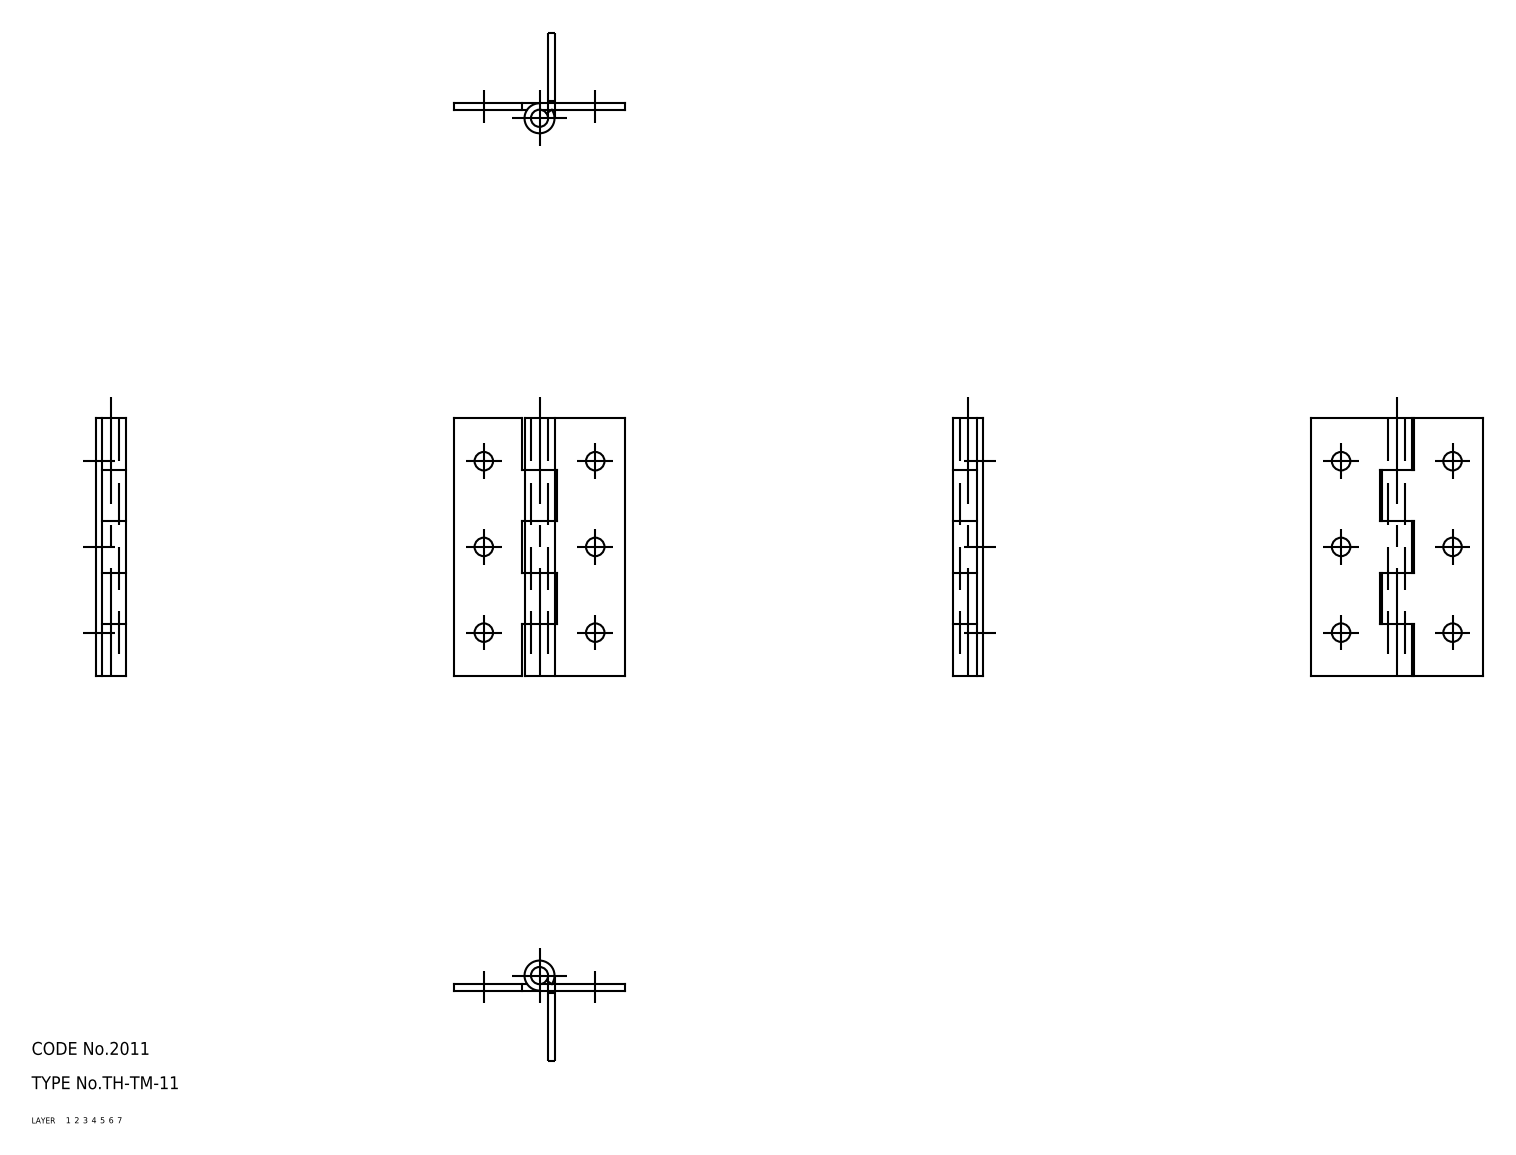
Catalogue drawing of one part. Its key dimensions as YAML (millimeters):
part_name: "hinge piece_B; hinge piece_A; shaft; TH_TM_11_20677_36"
step_written_by: "CADfix (AUTOMOTIVE_DESIGN)"
units: millimeters
bodies: {solids: 3, faces: 54, planar: 0, cylindrical: 0, other: 54}
overall_size: [60, 40, 7]
volume: 5177
surface_area: 7532
